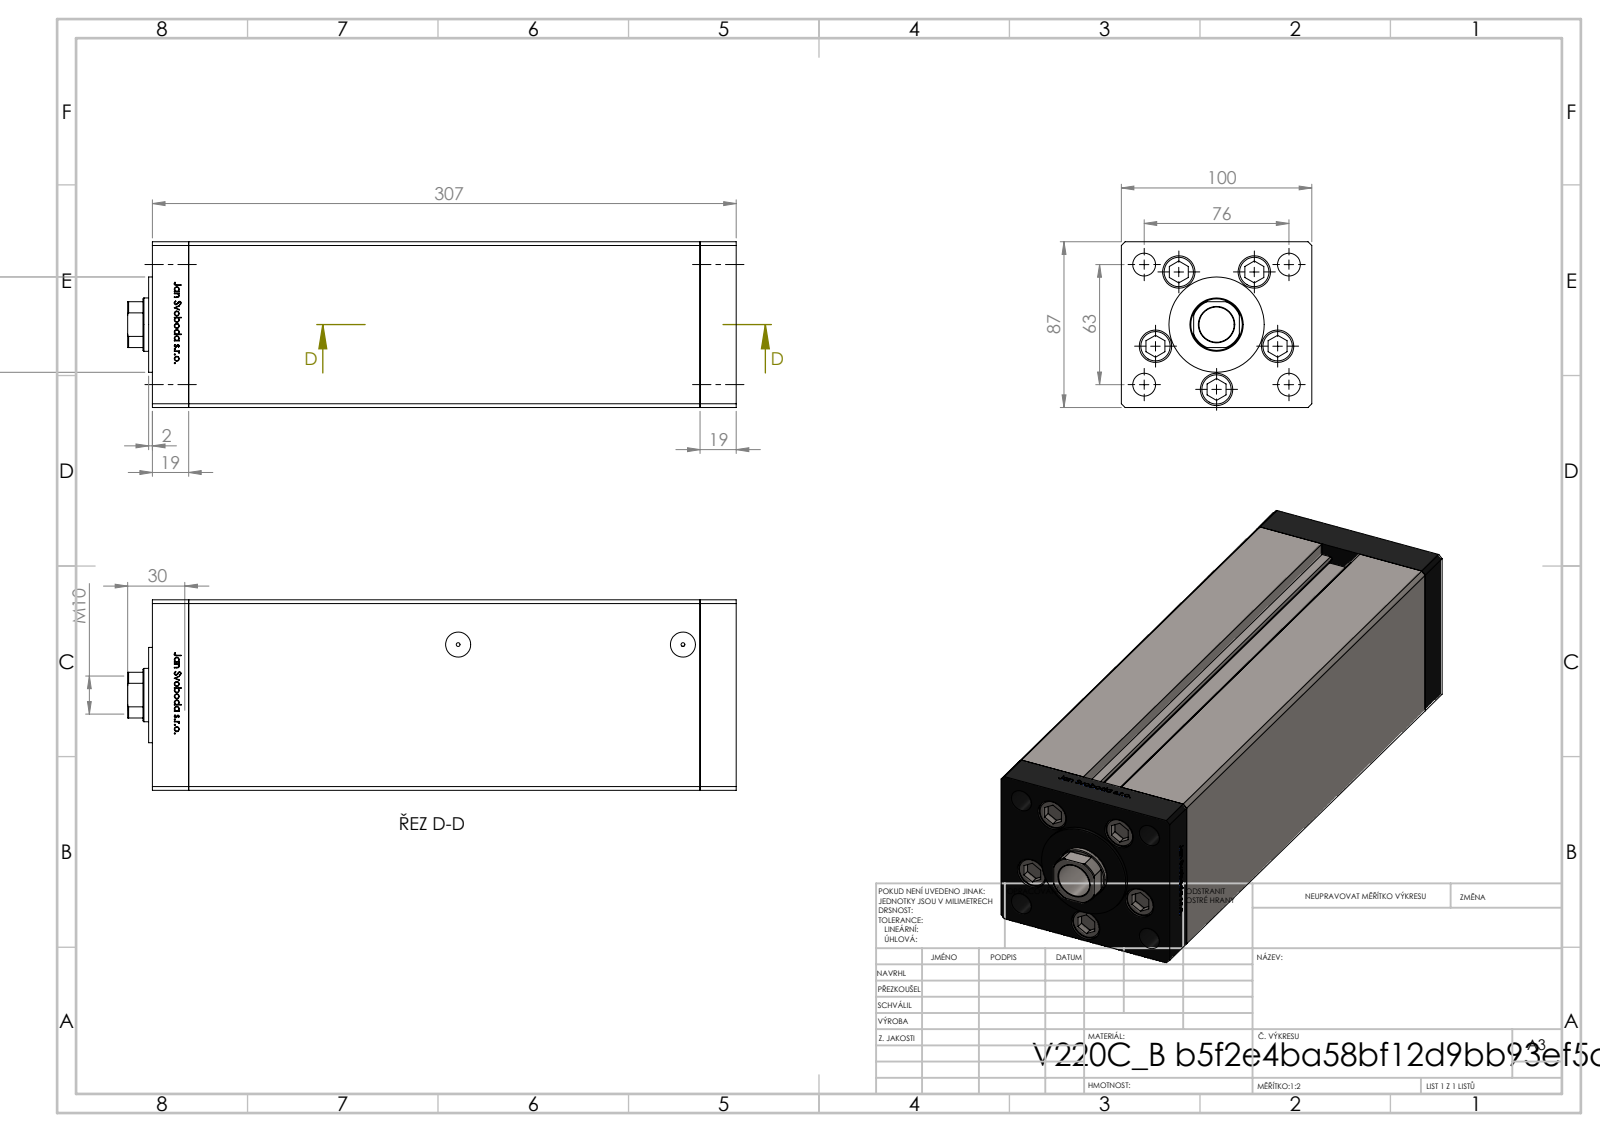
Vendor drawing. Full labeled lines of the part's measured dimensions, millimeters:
Part name (STEP PRODUCT): V220C_FRONT_B; V220C_B MIDDLE; ALLEN BOLT; V220C_VC_B (+1 more)
STEP written by: SolidWorks 2019 (CONFIG_CONTROL_DESIGN)
Units: millimetres
Bodies: 14 solids, 1185 faces (464 planar, 147 cylindrical, 574 other)
Overall size (bounding box): 319.5 × 100 × 87
Volume: 2 290 000 mm³ · Surface area: 281 980 mm²
Round holes (diameter × count): ⌀13.5 ×7, ⌀17 ×5, ⌀12 ×4, ⌀2 ×2, ⌀13.16 ×2, ⌀18.5 ×1, ⌀28 ×1
Round bosses / shafts (diameter × count): ⌀8 ×5, ⌀17 ×2, ⌀50 ×1
Partial cylindrical surfaces — rounded edges, fillets, slot ends (radius × count): R0.93 ×2, R13.5 ×1
Main face-to-face distances: 100, 87, 19, 268.5, 287.5, 34.25, 306.5, 15.25, 253.25, 272.25
Hole centre spacings: 34, 18.59, 39.64, 49.36, 57.95, 21.03, 38.08, 39.27
